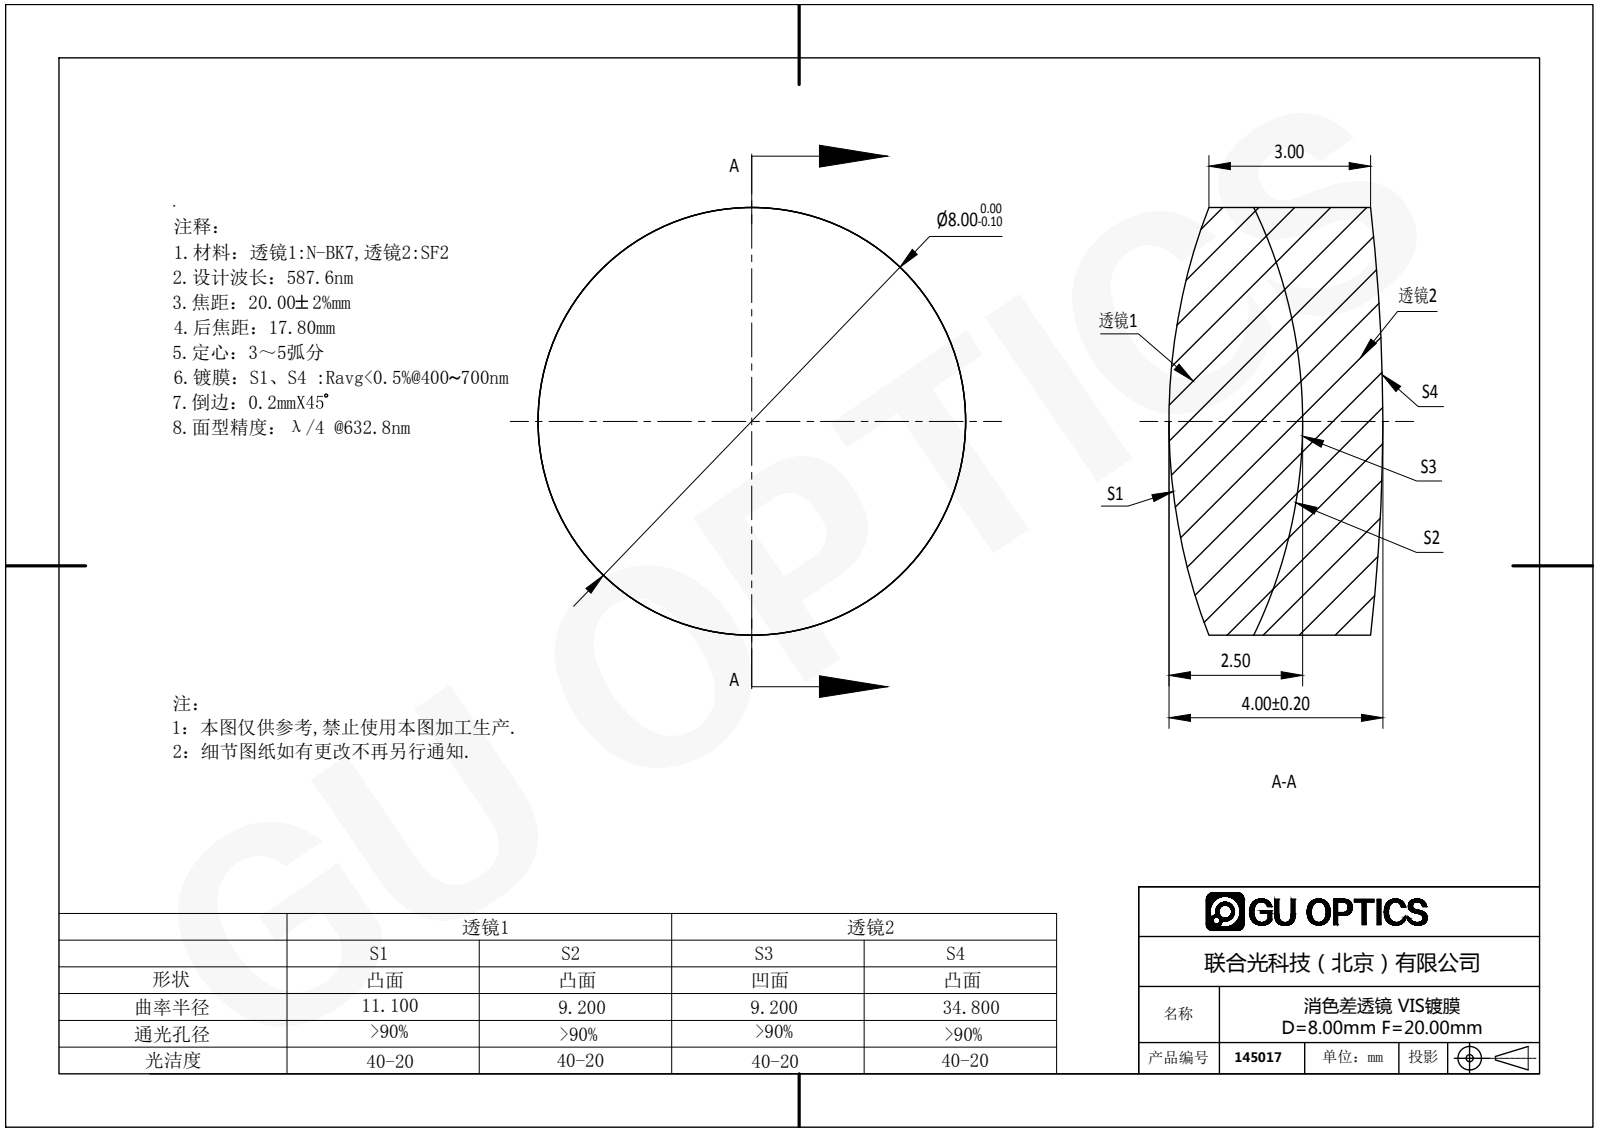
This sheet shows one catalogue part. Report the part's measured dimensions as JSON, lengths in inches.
{"part_name": "145017", "step_written_by": "SolidWorks 2016 (AUTOMOTIVE_DESIGN)", "units": "inches", "bodies": {"solids": 2, "faces": 12, "planar": 0, "cylindrical": 4, "other": 8}, "overall_size": [0.315, 0.315, 0.157], "volume_in3": 0.011, "surface_area_in2": 0.44, "round_bosses_or_shafts": [[0.315, 1]]}
